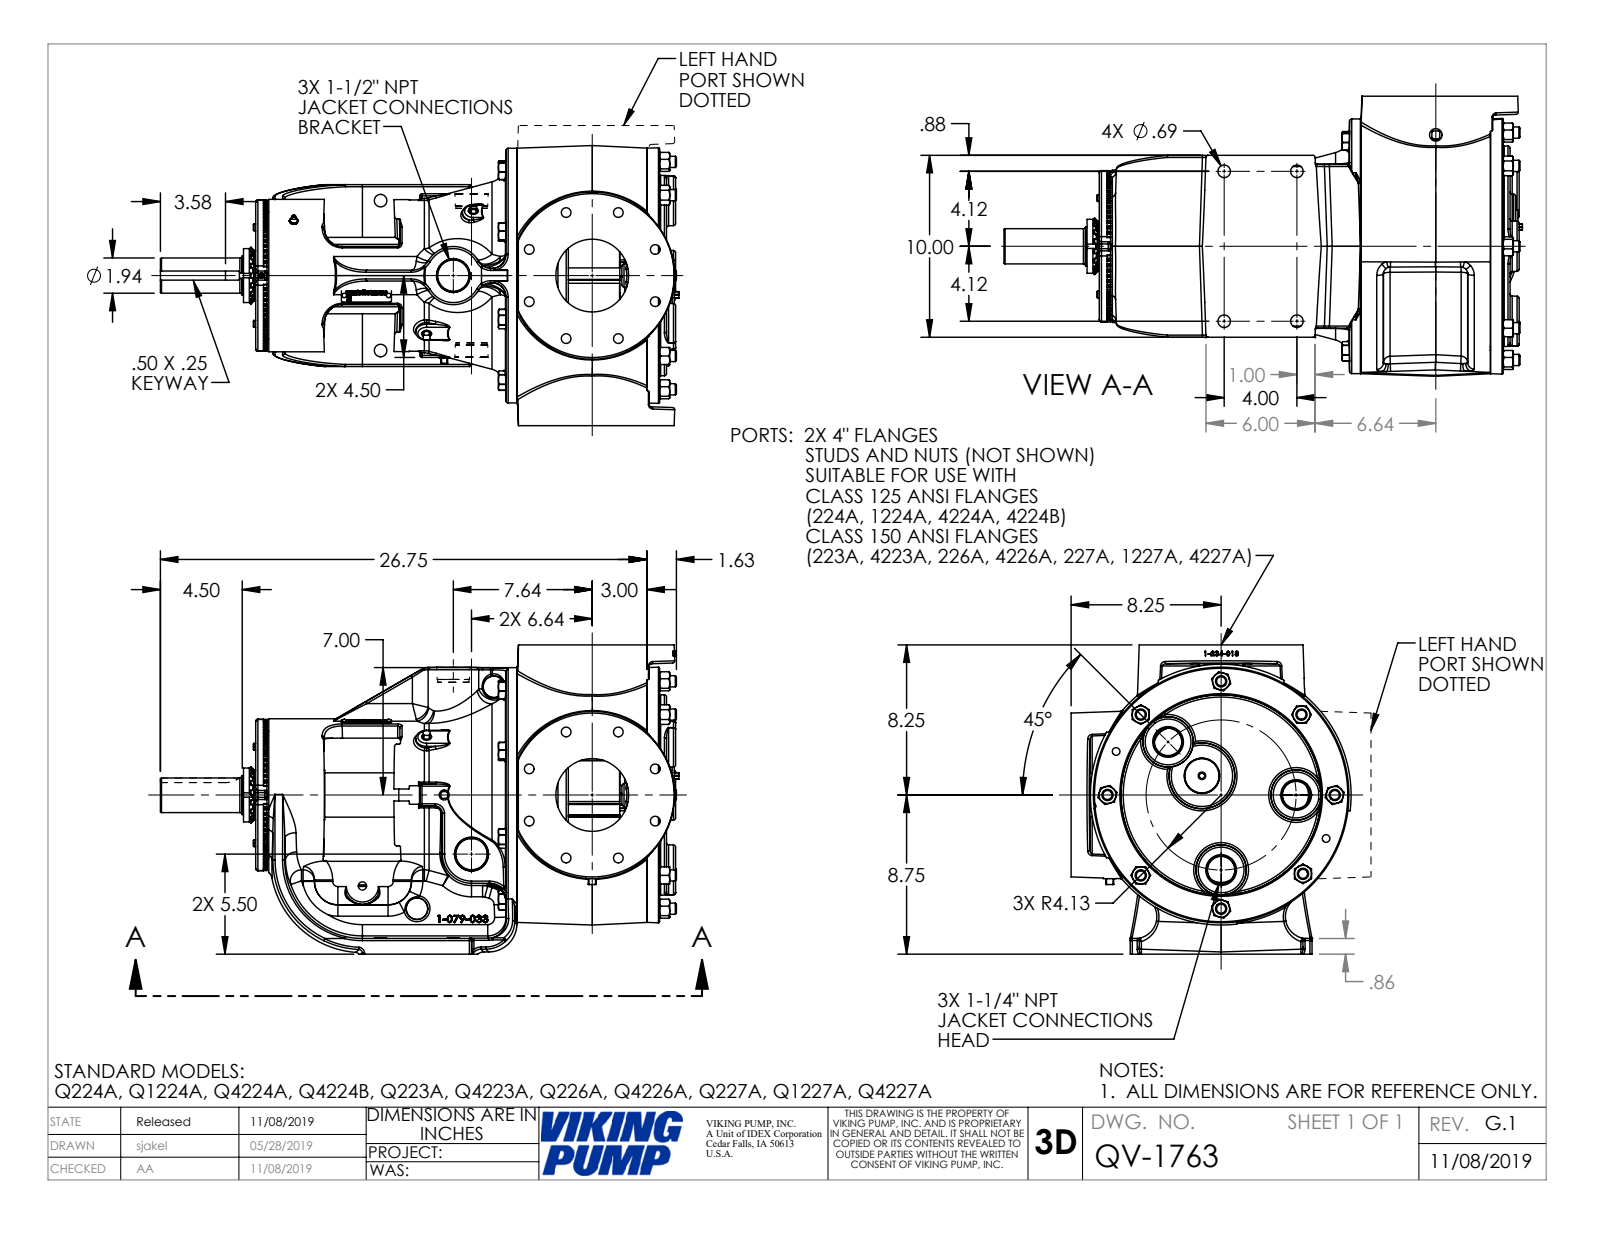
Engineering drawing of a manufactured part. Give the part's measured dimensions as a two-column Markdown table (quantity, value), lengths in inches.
| quantity | value |
| --- | --- |
| part name | QV-1763 |
| STEP written by | SolidWorks 2024 (AUTOMOTIVE_DESIGN) |
| units | inches |
| bodies | 1 solid, 2785 faces (1033 planar, 553 cylindrical, 1199 other) |
| overall size | 28.514 × 19.129 × 17.519 |
| volume | 2 396 in³ |
| surface area | 2 026 in² |
| round holes (diameter × count) | 1.157 × 8, 0.266 × 6, 0.531 × 4, 0.687 × 4, 0.313 × 2, 0.33 × 2, 0.453 × 1, 2.157 × 1, 2.167 × 1, 2.182 × 1, 2.765 × 1, 2.78 × 1 |
| round bosses / shafts (diameter × count) | 0.617 × 24, 0.625 × 14, 0.625 × 2, 0.375 × 2, 14 × 1, 8.38 × 1, 6.997 × 1, 6.749 × 1 |
| partial cylindrical surfaces (radius × count) | 0.12 × 74, 0.03 × 24, 0.015 × 18, 0.06 × 18, 0.092 × 18, 0.62 × 15, 0.25 × 8, 0.538 × 8 |
| main face-to-face distances | 0.38, 17, 3.75, 22.215, 22.595, 0.5, 18.465, 18.845, 2.4, 1 |
| hole center spacings | 2.079, 6.25, 8.839, 11.549, 5.783, 3.133, 3.6, 4.198 |
